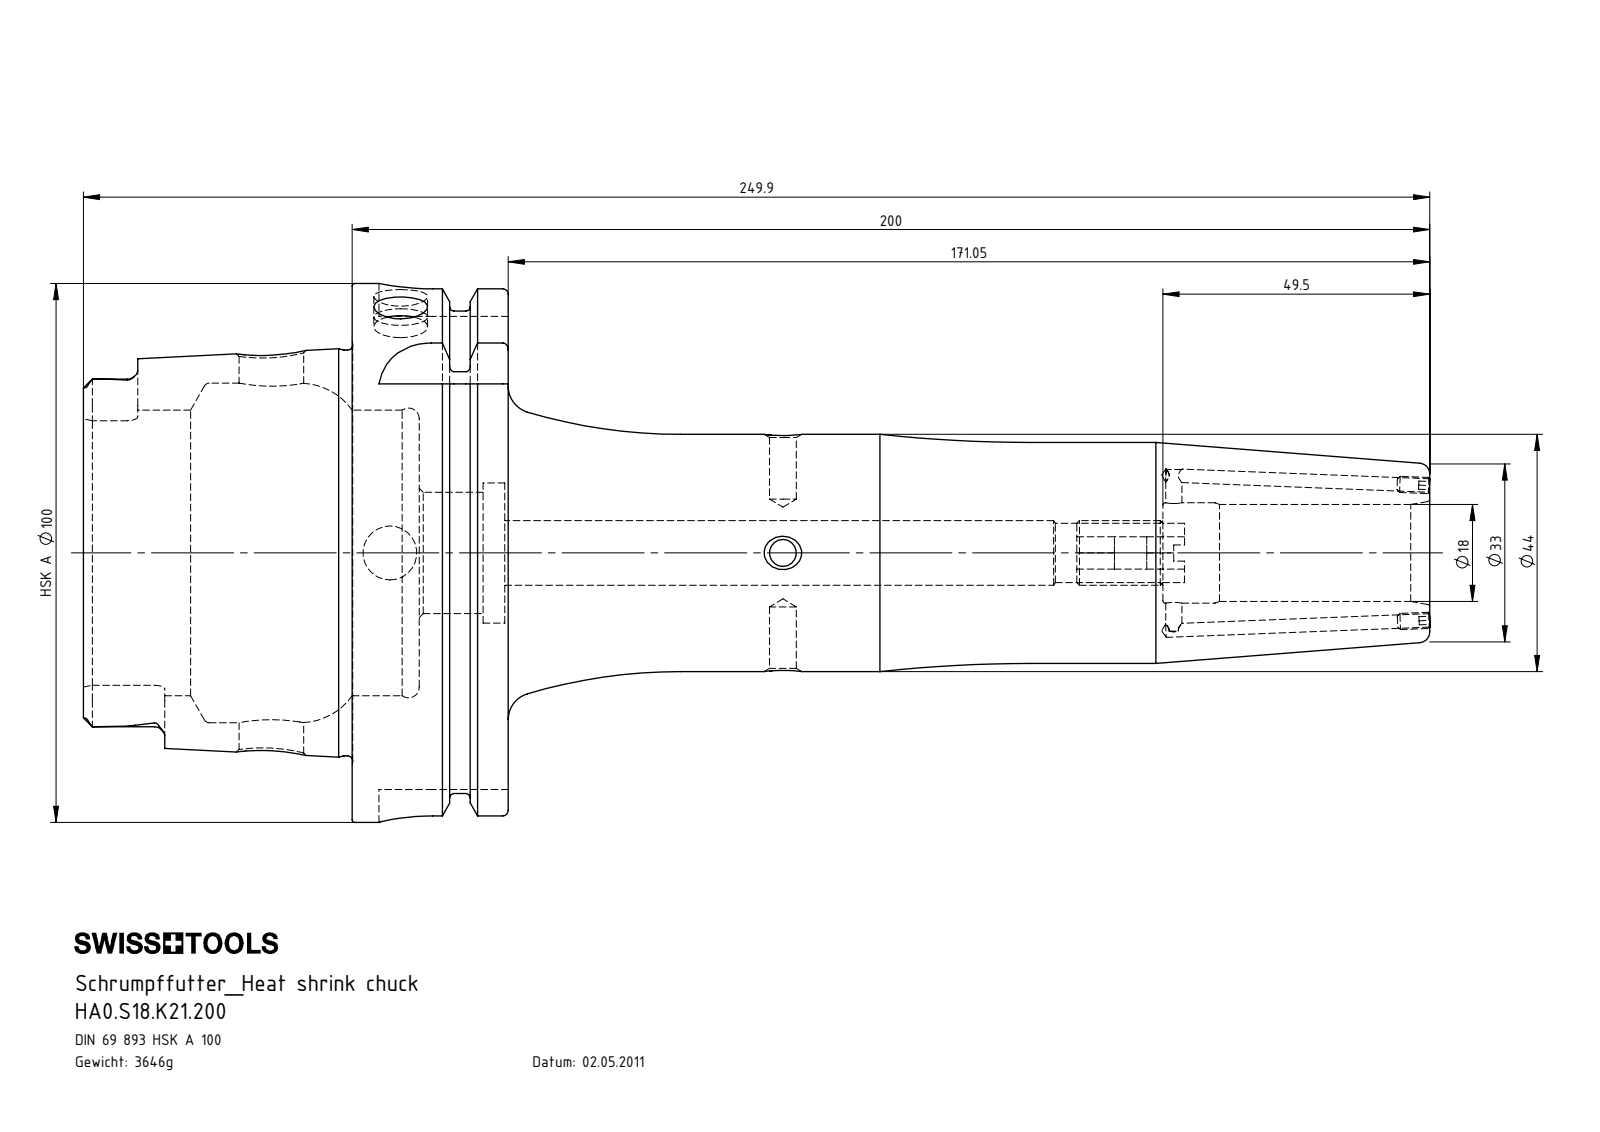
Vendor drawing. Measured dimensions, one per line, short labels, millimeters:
name: HA0-S18.K21.200_C_Fertigbearbeitung; ERU-AN5.K01.020_A; ERU-CJ2.001.006; HA0.S18.K21.200
written by: SolidWorks 2017 (CONFIG_CONTROL_DESIGN)
unit: mm
bodies: 4 solids, 307 faces (95 planar, 89 cylindrical, 123 other)
size: 249.98 × 100 × 100
volume: 464 483 mm³; area: 80 878 mm²
holes: 3× ⌀10, 2× ⌀2.5, 2× ⌀5, 2× ⌀12, 1× ⌀3, 1× ⌀6, 1× ⌀11, 1× ⌀18, 1× ⌀18.6, 1× ⌀22.5, 1× ⌀26, 1× ⌀53
bosses: 2× ⌀3, 1× ⌀100, 1× ⌀91.95, 1× ⌀75.26, 1× ⌀44, 1× ⌀41
rounds: 6× R1.9, 4× R4.88, 4× R10
face distances: 28.95, 12.45, 16.5, 49.9, 62.35, 78.85, 87.8, 15.85, 78.2, 28.3
hole spacings: 72.55, 72.95, 94.95, 167.5
